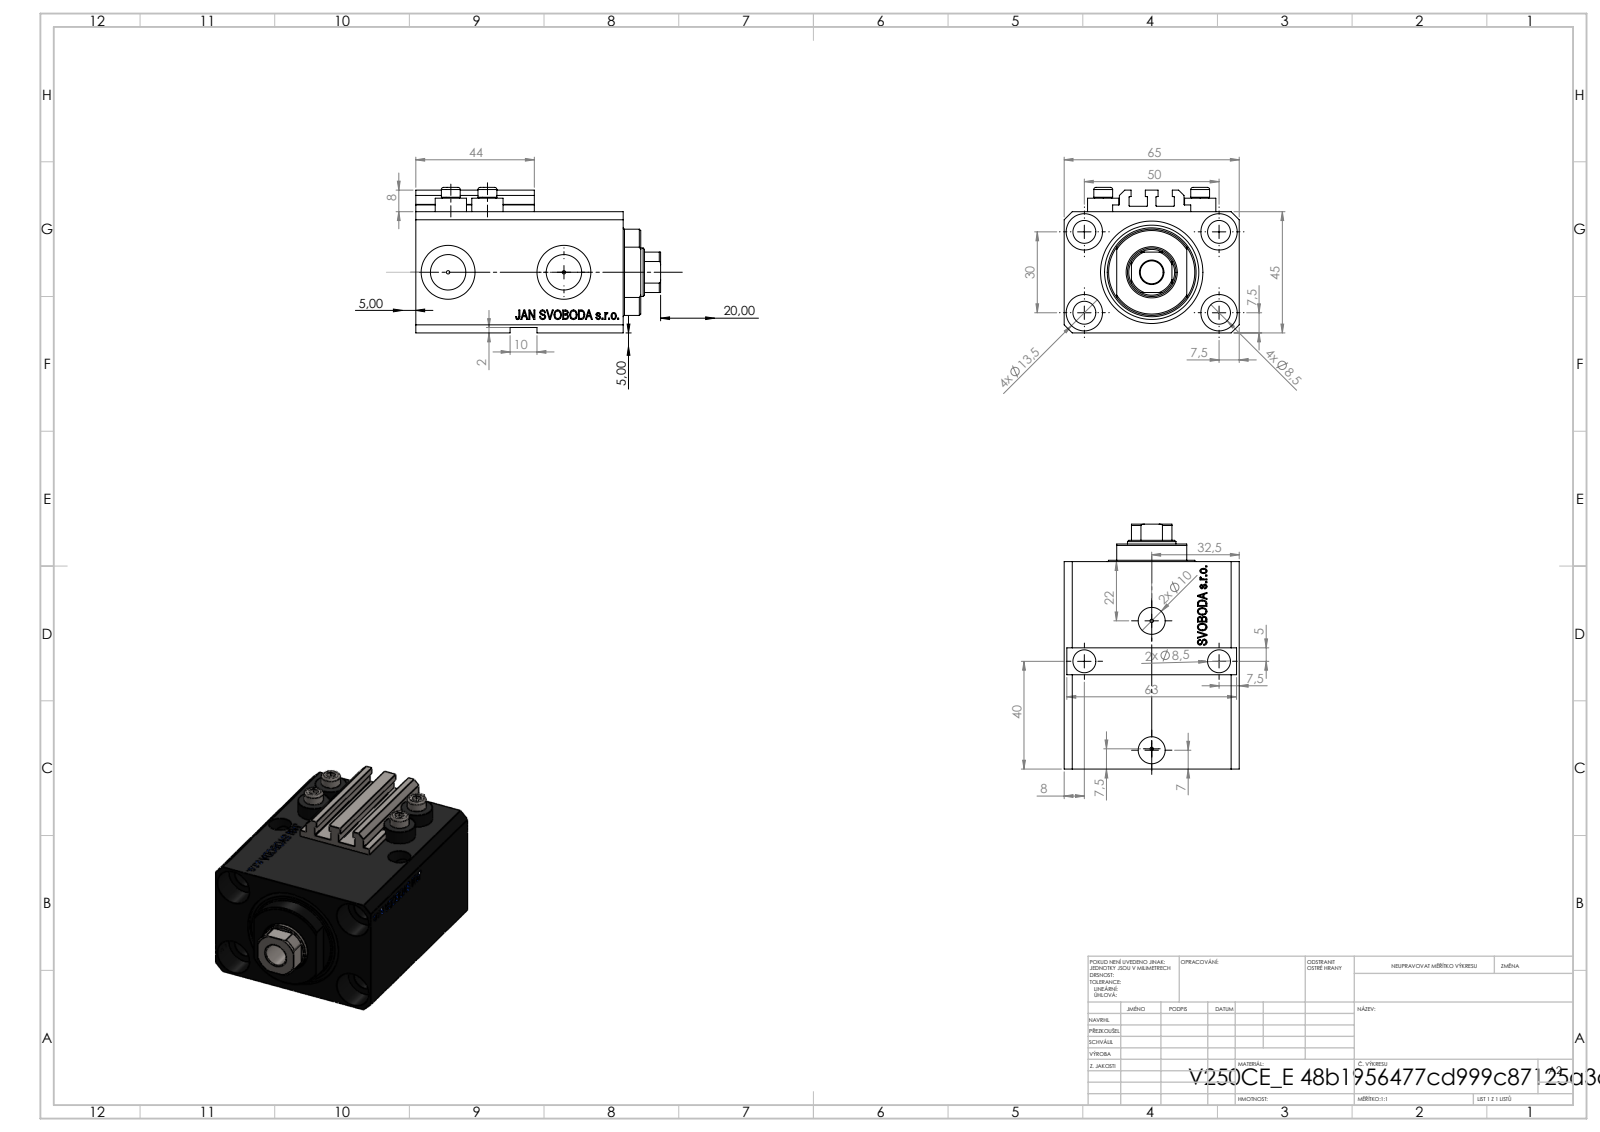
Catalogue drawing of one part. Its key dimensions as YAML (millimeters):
part_name: "V250CE_C_VCP; V250CE_E_Body; V250CE_VC_E; ALLEN BOLT V250CE"
step_written_by: "SolidWorks 2019 (CONFIG_CONTROL_DESIGN)"
units: millimeters
bodies: {solids: 8, faces: 1067, planar: 511, cylindrical: 126, other: 430}
overall_size: [91, 65, 54]
volume: 199775
surface_area: 59185
round_holes:
  - {diameter: 8.5, count: 7}
  - {diameter: 1.25, count: 4}
  - {diameter: 4, count: 4}
  - {diameter: 13.5, count: 4}
  - {diameter: 10, count: 2}
  - {diameter: 13.16, count: 2}
  - {diameter: 20, count: 2}
  - {diameter: 18, count: 1}
  - {diameter: 25, count: 1}
  - {diameter: 38, count: 1}
round_bosses_or_shafts:
  - {diameter: 11.6, count: 4}
  - {diameter: 7, count: 4}
partial_cylinders:
  - {radius: 0.2, count: 10}
  - {radius: 8.5, count: 1}
  - {radius: 16, count: 1}
face_to_face_distances: [45, 65, 63, 14, 77, 2, 6.9, 56.1, 70.1, 47]
hole_center_spacings: [29.15, 50, 13.6, 15.12, 18.81, 18.97, 26.22, 26.61]
